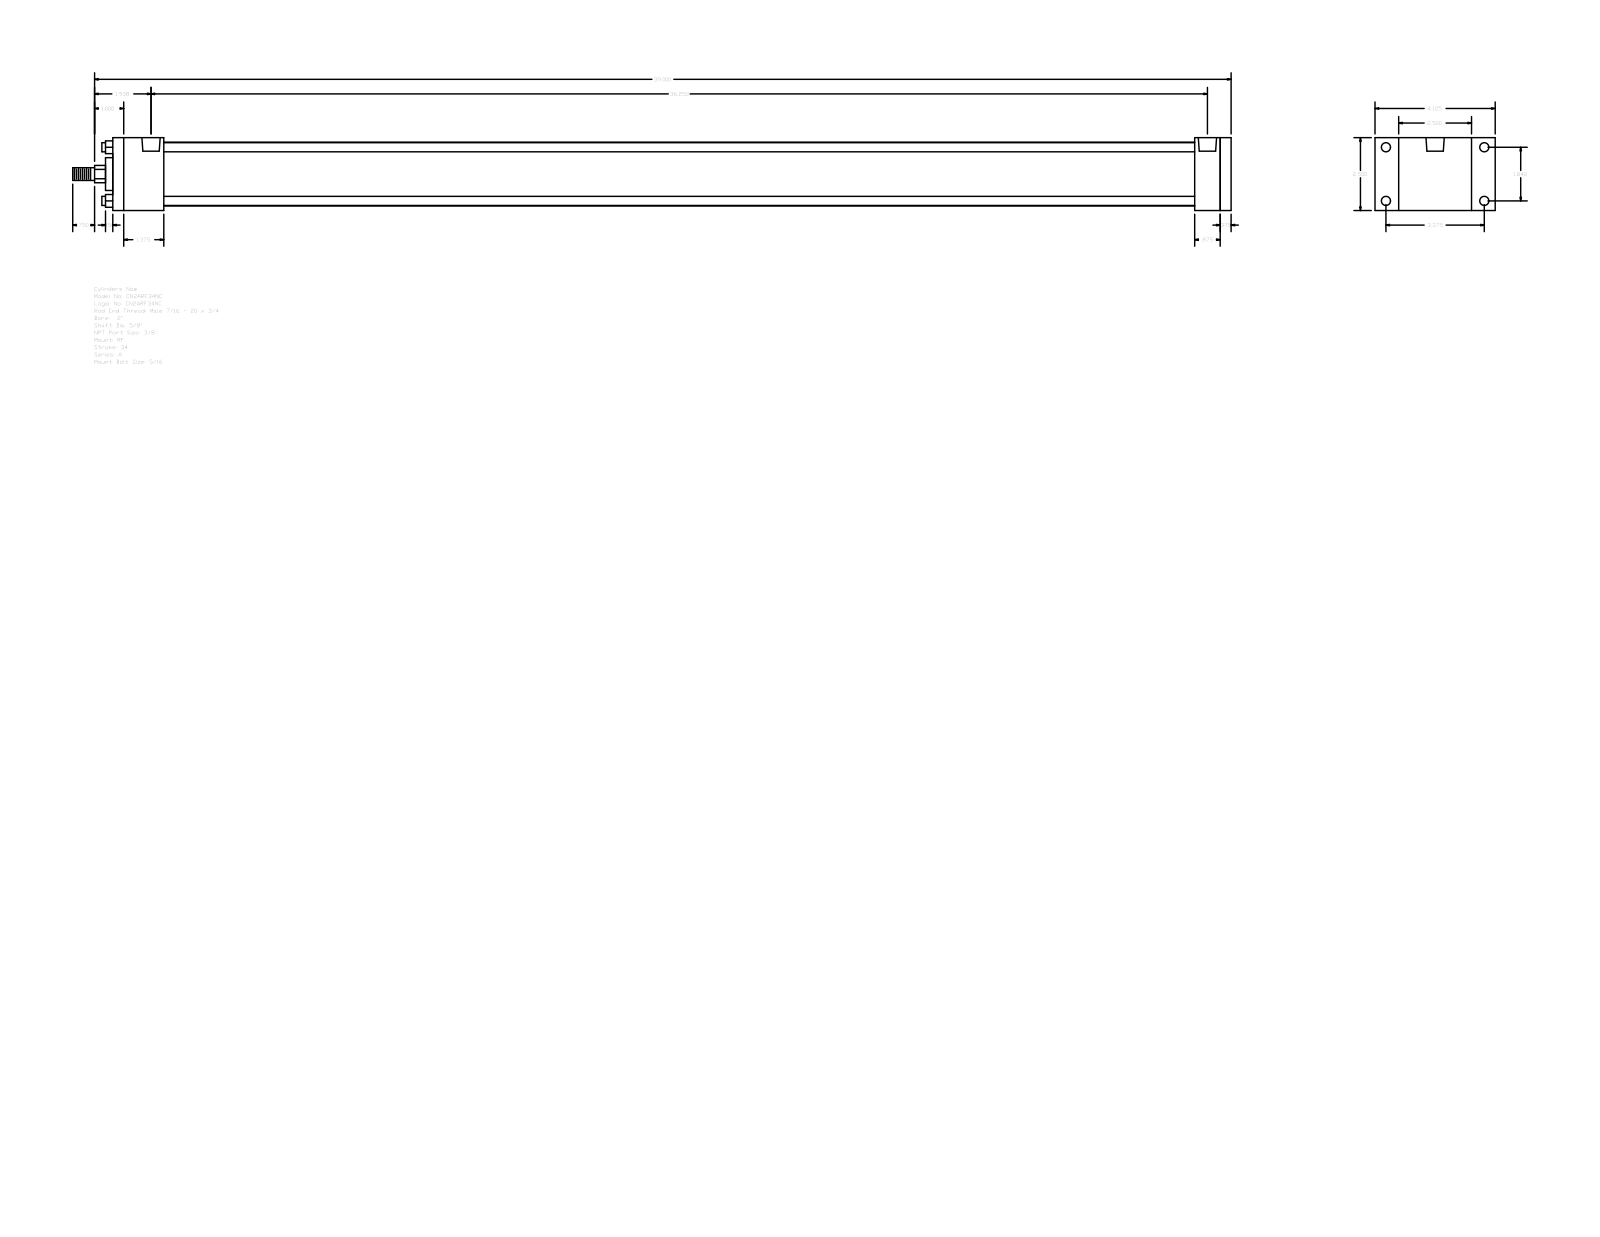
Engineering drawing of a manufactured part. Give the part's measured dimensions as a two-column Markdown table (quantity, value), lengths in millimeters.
| quantity | value |
| --- | --- |
| part name | A_RF__0200_0.625 |
| STEP written by | GSSL Pune (CONFIG_CONTROL_DESIGN) |
| units | millimeters |
| bodies | 0 solids, 92 faces (64 planar, 28 cylindrical, 0 other) |
| overall size | 1009.65 × 104.78 × 63.5 |
| round holes (diameter × count) | 5.56 × 4, 7.94 × 4, 15.93 × 2 |
| round bosses / shafts (diameter × count) | 7.94 × 4, 55.63 × 1, 28.57 × 1, 15.88 × 1, 11.11 × 1 |
| partial cylindrical surfaces (radius × count) | 7.54 × 1 |
| main face-to-face distances | 63.5, 974.72, 965.2, 9.52, 44.45, 920.75, 930.27, 942.97, 898.52, 22.23 |
| hole center spacings | 46.74, 85.72, 97.63, 912.8, 3.97, 3.98, 916.77, 916.78 |
